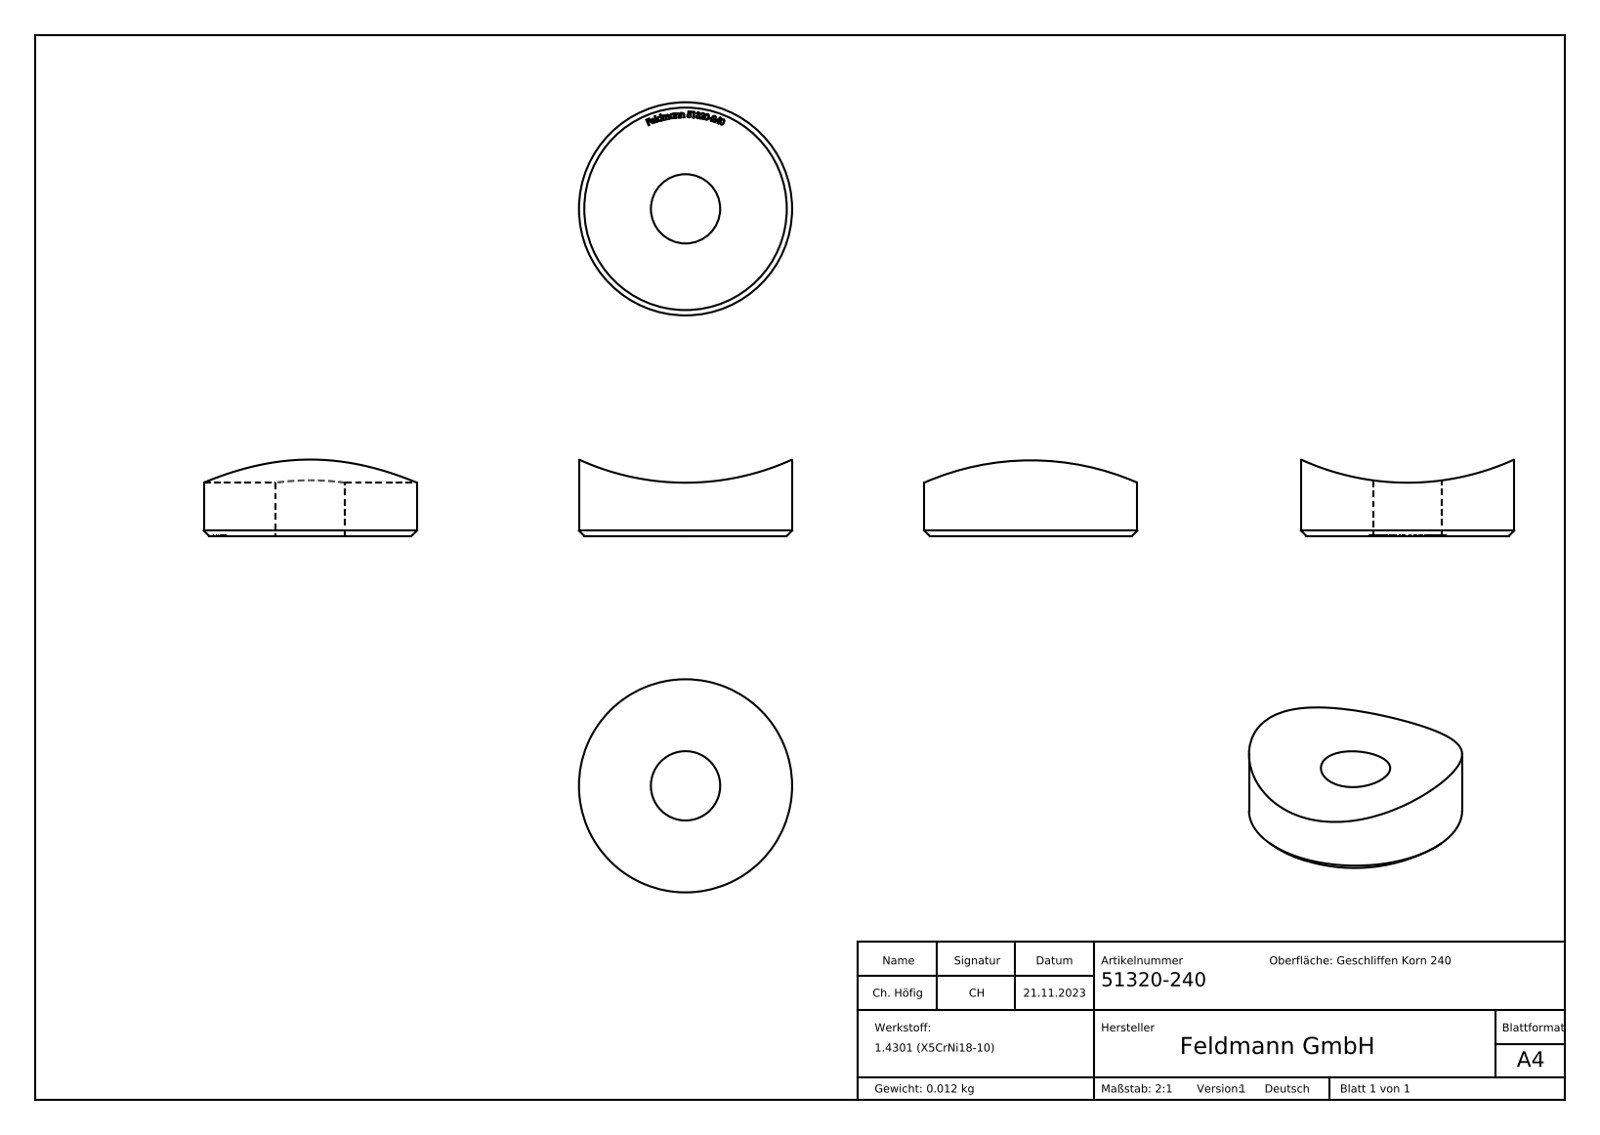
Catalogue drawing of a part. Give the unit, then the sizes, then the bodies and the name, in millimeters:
Units: millimetres
Overall size (bounding box): 20 × 20 × 7.17
Round holes (diameter × count): ⌀6.5 ×1
Round bosses / shafts (diameter × count): ⌀20 ×1
Partial cylindrical surfaces — rounded edges, fillets, slot ends (radius × count): R24.15 ×1
Main face-to-face distances: 0.34, 0.31, 0.39, 0.53, 0.36, 0.55, 0.54
Volume: 1 561 mm³ · Surface area: 1 040 mm²
Bodies: 1 solid, 226 faces (122 planar, 3 cylindrical, 101 other)
Part name (STEP PRODUCT): 51320-240
STEP written by: SolidWorks 2018 (CONFIG_CONTROL_DESIGN)
